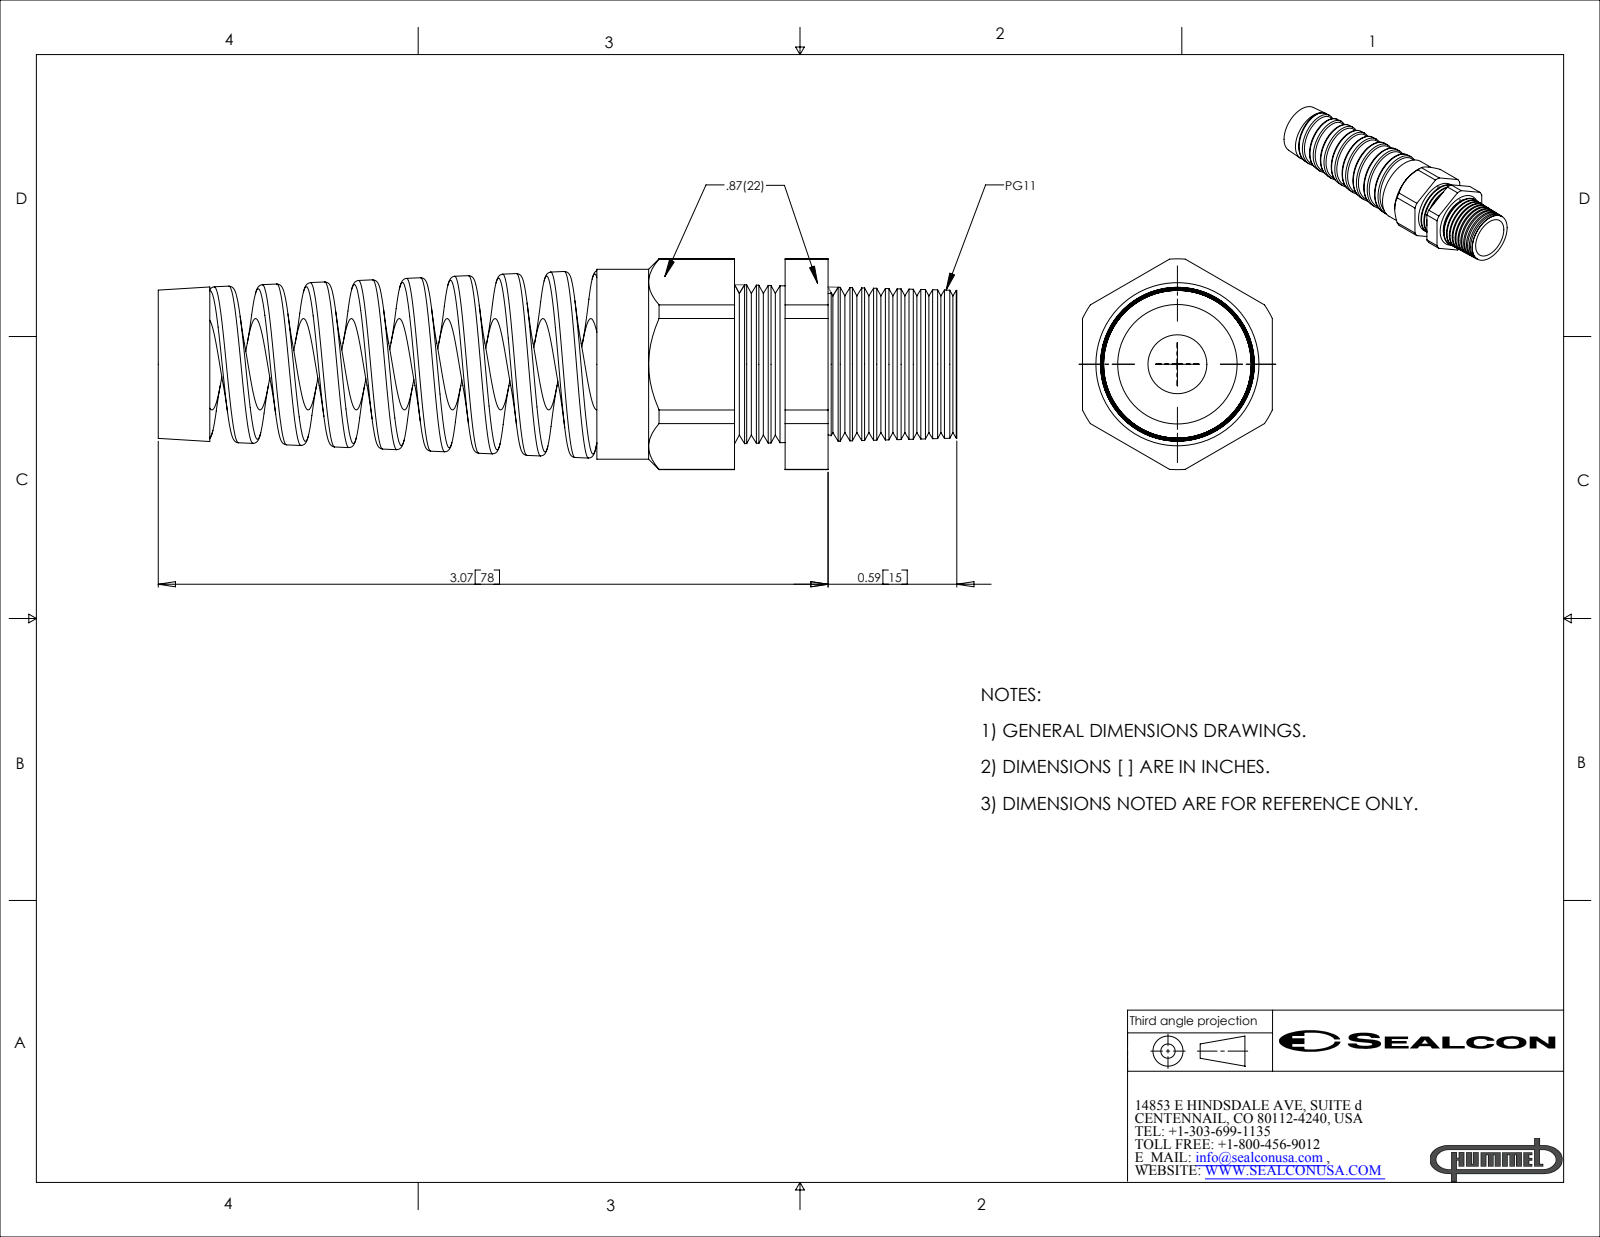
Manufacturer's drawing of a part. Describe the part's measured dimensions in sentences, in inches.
The part is named "CF11CR-BK". Its 3-D file was written by "SolidWorks 2007 (CONFIG_CONTROL_DESIGN)". It is 2 solids with 196 faces: 24 planar, 42 cylindrical and 130 other. Overall it measures 3.66 by 0.966 by 0.87 inches. Its volume is 1.017 cubic inches and its surface area 19.35 square inches. Round holes: 1 of diameter 0.27, 1 of diameter 0.419, 1 of diameter 0.448. Round bosses or shafts: 1 of diameter 0.87, 1 of diameter 0.547. Partial cylindrical surfaces (rounded edges, fillets, slot ends): 1 of radius 0.483. The main face-to-face distances are 0.87, 0.626, 0.394, 0.232, 0.237, 0.631, 0.863, 1.06, 0.823, 0.429.
